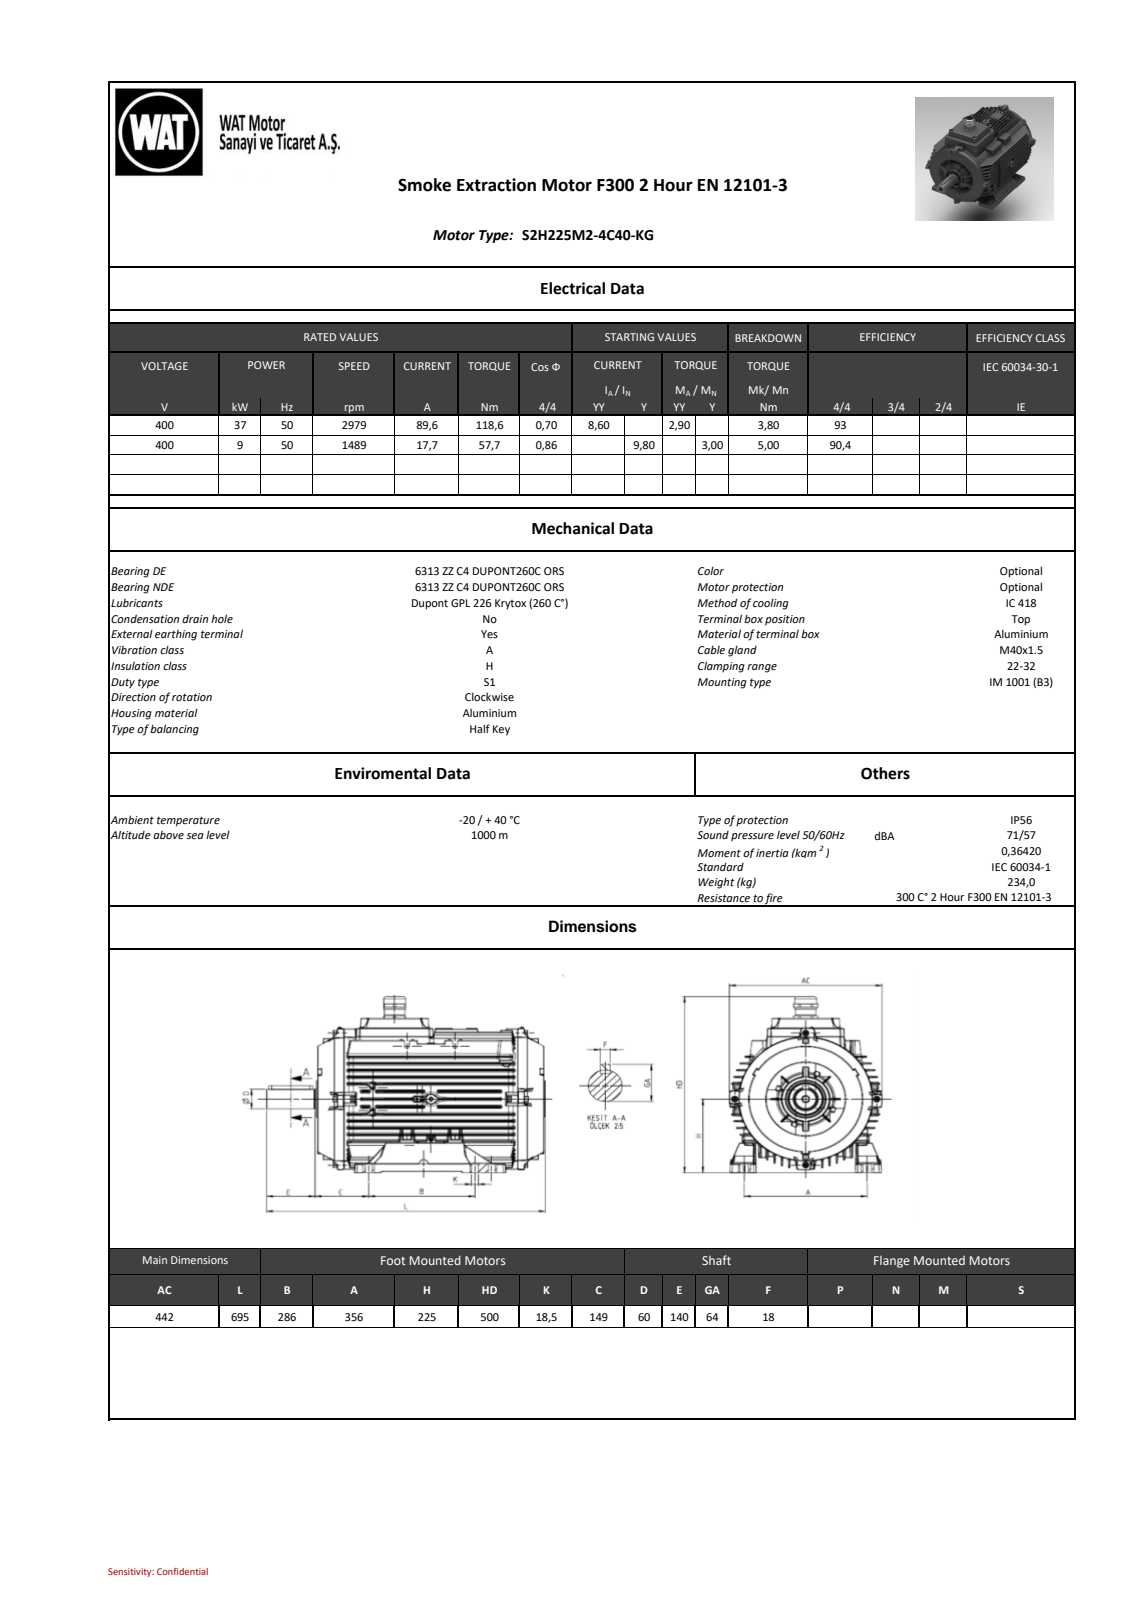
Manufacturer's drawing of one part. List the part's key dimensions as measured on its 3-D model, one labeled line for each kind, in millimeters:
Part name (STEP PRODUCT): AD_objects
STEP written by: SIEMENS PLM Software NX2206.8101 (AP203_CONFIGURATION_CONTROLLED_3D_DESIGN_OF_MECHANICAL_PARTS_AND_ASSEMBLIES_MIM_LF)
Units: millimetres
Bodies: 0 solids, 3544 faces (1068 planar, 934 cylindrical, 1542 other)
Overall size (bounding box): 695 × 501 × 442
Round holes (diameter × count): ⌀10.3 ×3, ⌀17.5 ×1, ⌀21 ×1, ⌀32 ×1, ⌀65.2 ×1, ⌀208 ×1, ⌀236 ×1
Round bosses / shafts (diameter × count): ⌀16 ×8, ⌀12 ×4, ⌀353 ×1, ⌀65.3 ×1, ⌀60 ×1, ⌀59.4 ×1, ⌀49.5 ×1, ⌀46.84 ×1
Partial cylindrical surfaces — rounded edges, fillets, slot ends (radius × count): R1 ×280, R2 ×183, R0.5 ×73, R2.5 ×50, R0.8 ×37, R0.6 ×19, R4 ×18, R2.6 ×16
Main face-to-face distances: 189.81, 15.53, 169.04, 20.77, 14.83, 184.57, 5.24, 24.63, 39.58, 150.23
Hole centre spacings: 167.04, 215
